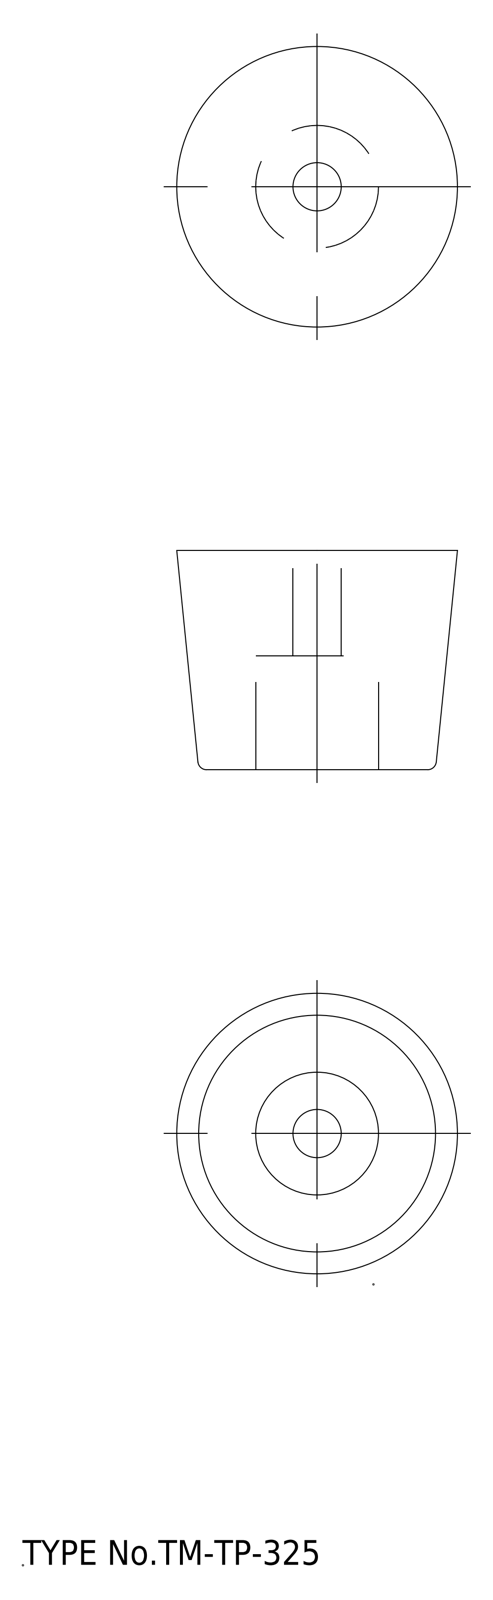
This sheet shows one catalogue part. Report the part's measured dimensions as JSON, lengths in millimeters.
{"step_written_by": "spGate 19.8.4 (****-****-****-****) (AUTOMOTIVE_DESIGN)", "units": "millimeters", "bodies": {"solids": 1, "faces": 11, "planar": 3, "cylindrical": 4, "other": 4}, "overall_size": [32, 32, 25], "volume_mm3": 14862, "surface_area_mm2": 4411, "round_holes": [[5.5, 1], [14, 1]], "face_to_face_distances": [25, 13, 12]}
